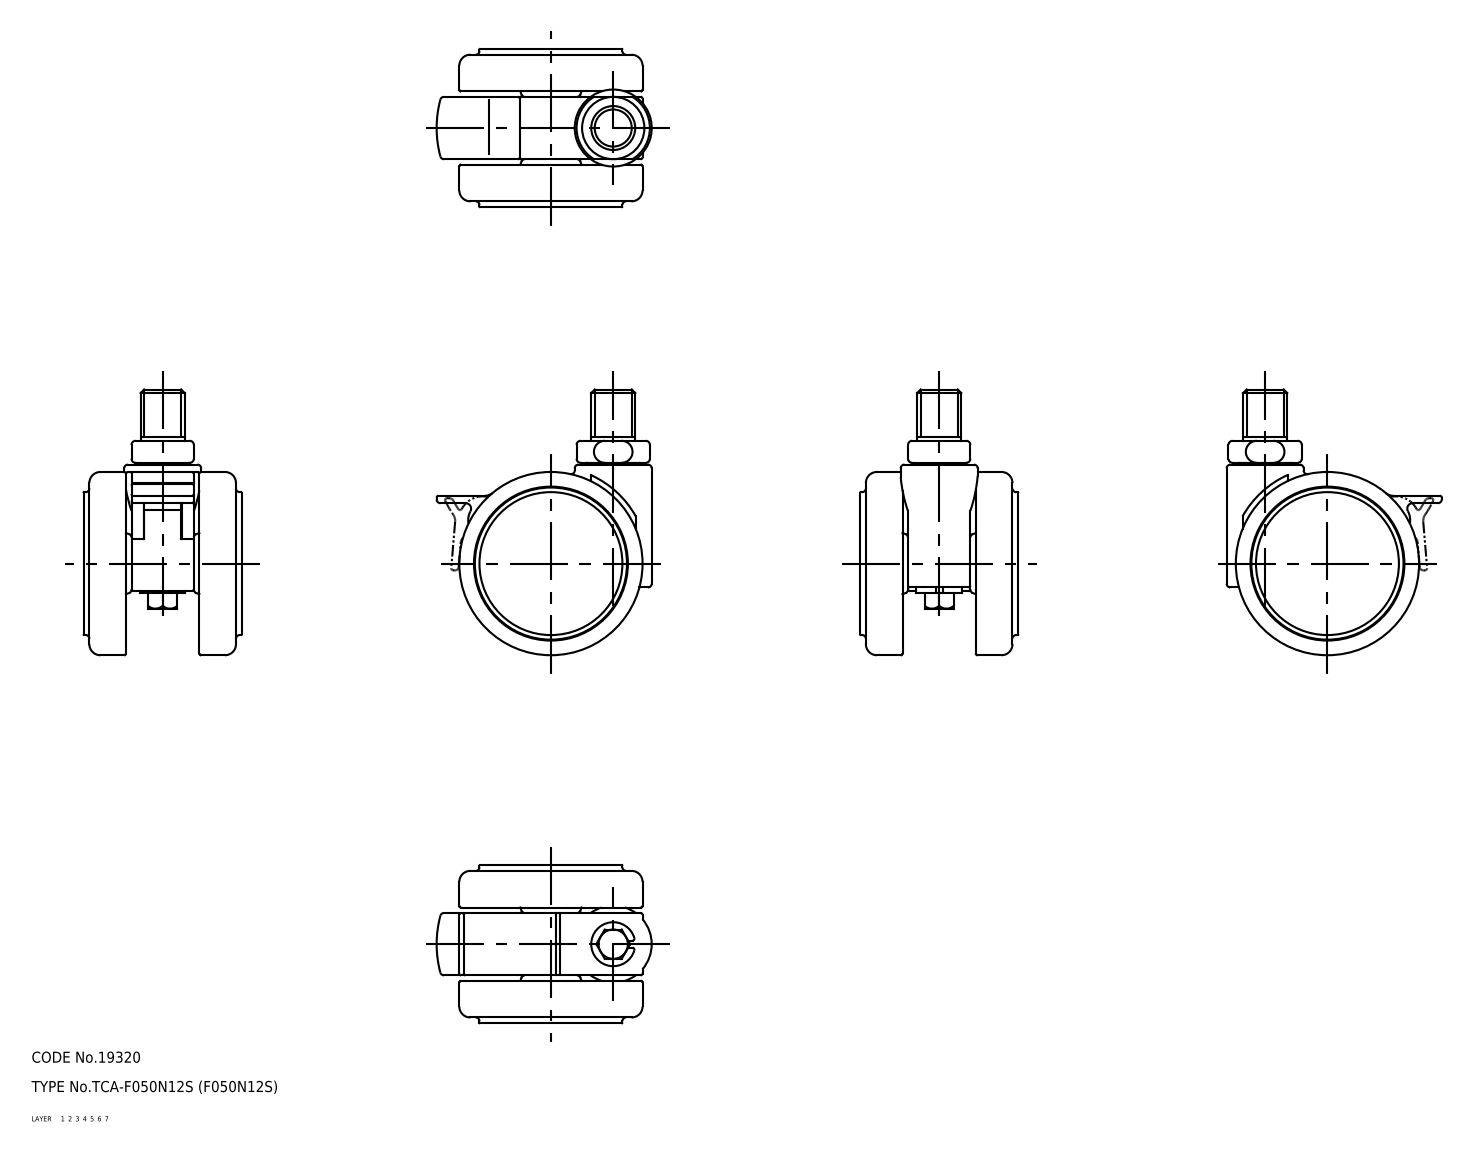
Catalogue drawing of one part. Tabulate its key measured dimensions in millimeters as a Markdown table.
| quantity | value |
| --- | --- |
| part name | 67123553; 67123566; 67123579; 67123592 (+1 more) |
| STEP written by | CADfix (AUTOMOTIVE_DESIGN) |
| units | millimeters |
| bodies | 5 solids, 246 faces (0 planar, 0 cylindrical, 246 other) |
| overall size | 72.5 × 58.69 × 43.2 |
| volume | 59 770 mm³ |
| surface area | 23 266 mm² |
